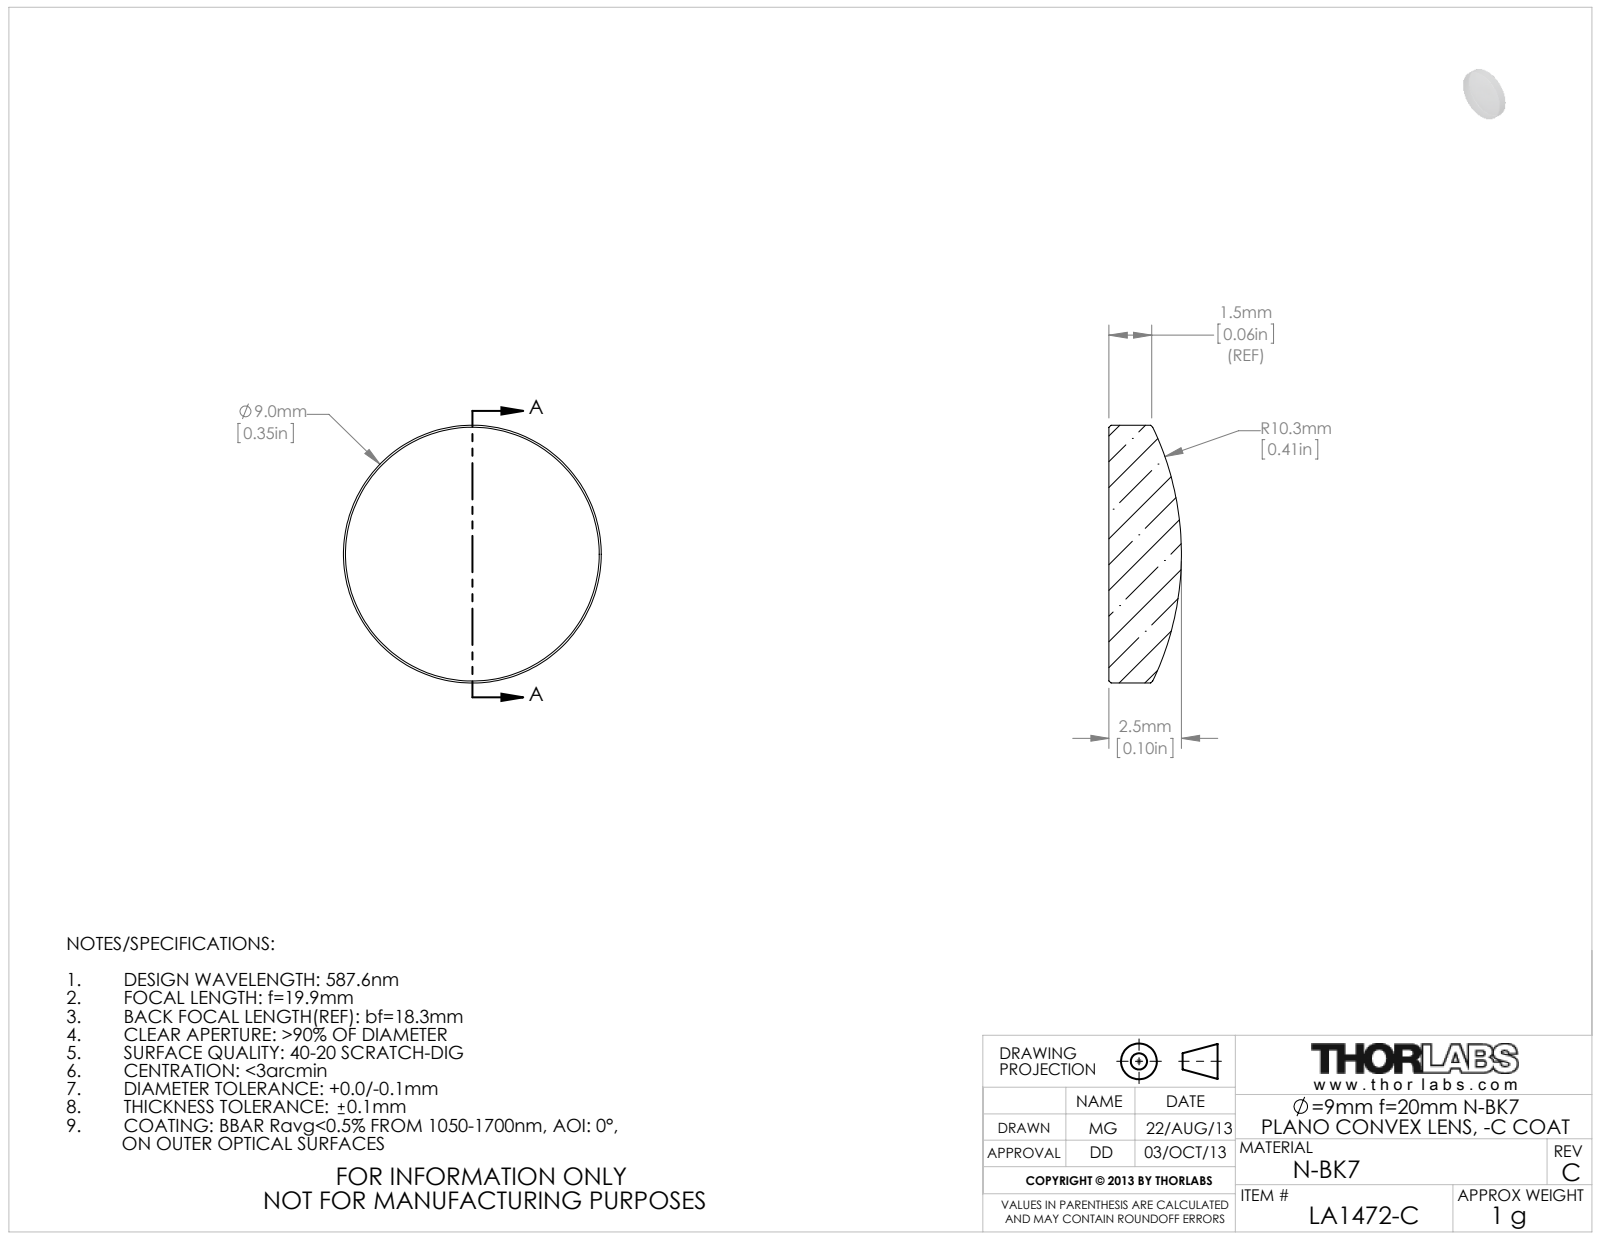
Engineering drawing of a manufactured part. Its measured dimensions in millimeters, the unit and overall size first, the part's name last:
Units: millimetres
Overall size (bounding box): 9 × 9 × 2.53
Round bosses / shafts (diameter × count): ⌀9 ×1
Volume: 129 mm³ · Surface area: 173 mm²
Bodies: 1 solid, 5 faces (1 planar, 2 cylindrical, 2 other)
Part name (STEP PRODUCT): 4567-E0W
STEP written by: SolidWorks 2009 (AUTOMOTIVE_DESIGN)
